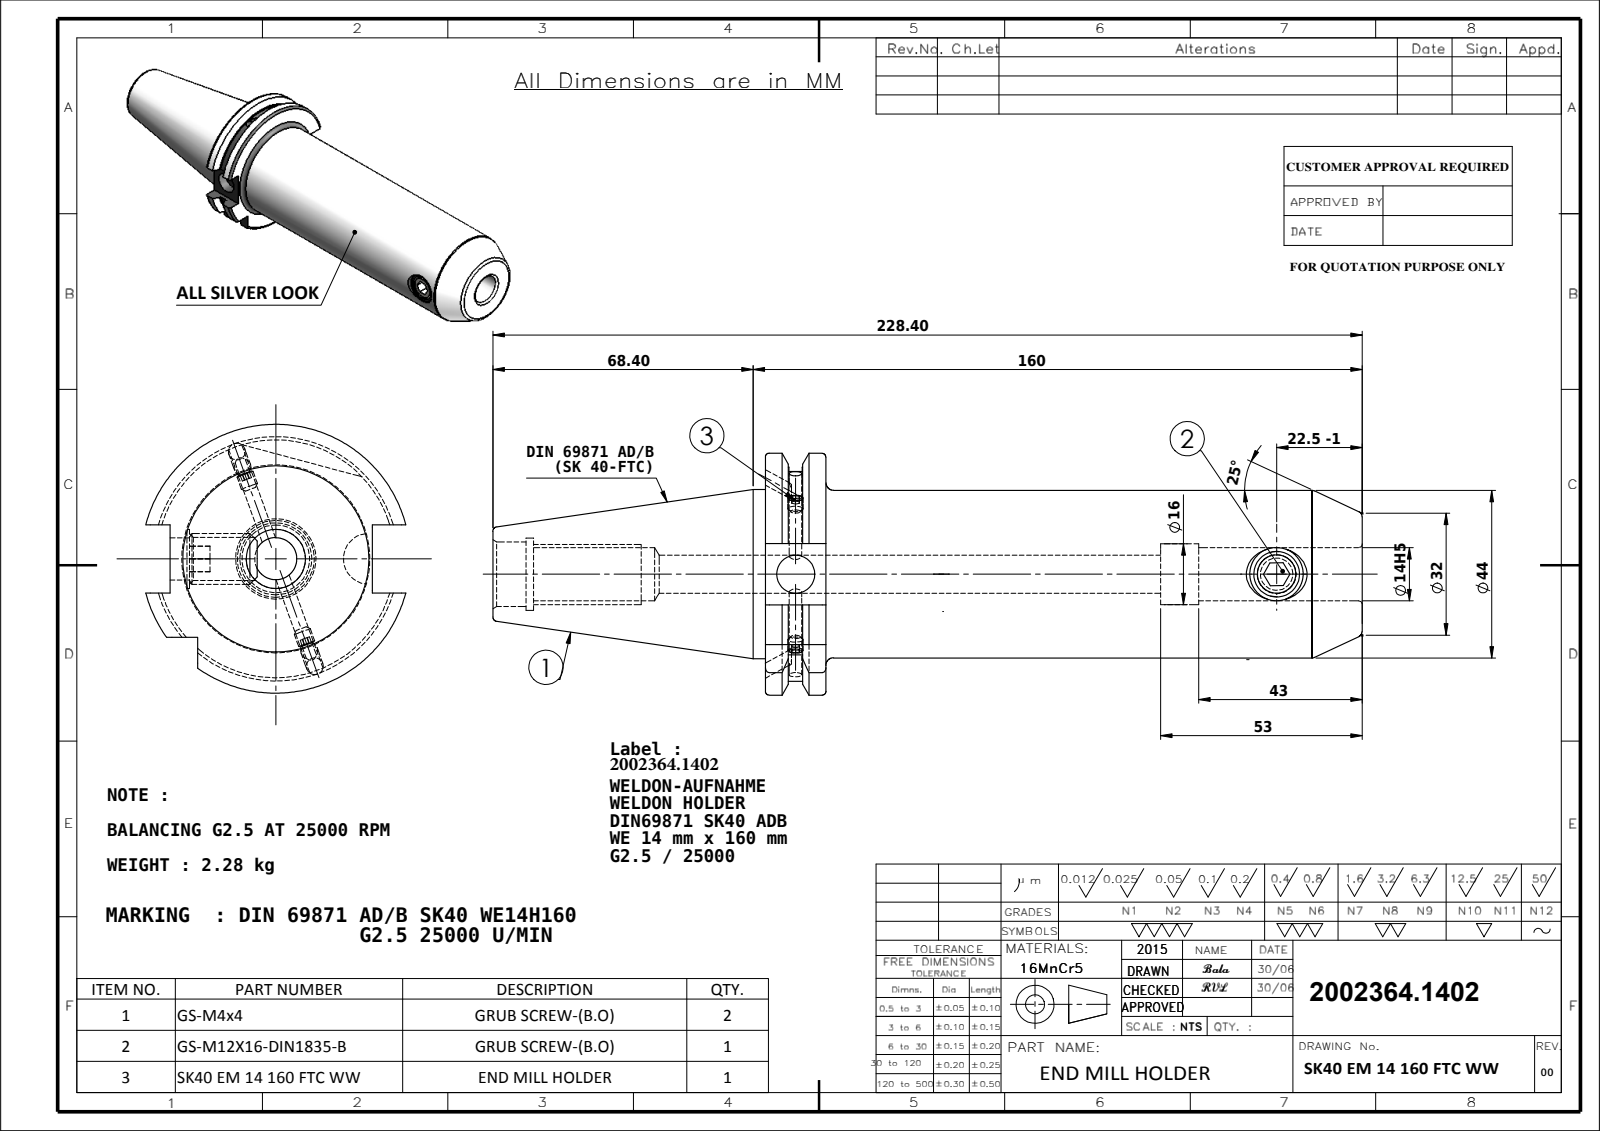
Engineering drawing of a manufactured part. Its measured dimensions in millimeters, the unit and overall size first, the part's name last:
Units: millimetres
Overall size (bounding box): 228.4 × 63.55 × 61.48
Round holes (diameter × count): ⌀10 ×2, ⌀14 ×2, ⌀3.3 ×1, ⌀10.2 ×1, ⌀16 ×1, ⌀17 ×1, ⌀19 ×1
Round bosses / shafts (diameter × count): ⌀4 ×2, ⌀44.45 ×1, ⌀44 ×1, ⌀12 ×1
Partial cylindrical surfaces — rounded edges, fillets, slot ends (radius × count): R28.12 ×1, R31.77 ×1
Main face-to-face distances: 15.9, 156.8, 140.9, 16.1, 47.8, 4.6, 43.2, 71.6, 87.5, 228.4
Hole centre spacings: 126.35
Volume: 295 458 mm³ · Surface area: 46 066 mm²
Bodies: 4 solids, 160 faces (58 planar, 44 cylindrical, 58 other)
Part name (STEP PRODUCT): 91406-WE714160; SK40 EM 14 160 FTC WW; M12X16._ISO 4026 - M12 x 12-N; M4X4_DIN 913 - M4 x 4-N
STEP written by: SolidWorks 2009 (CONFIG_CONTROL_DESIGN)
